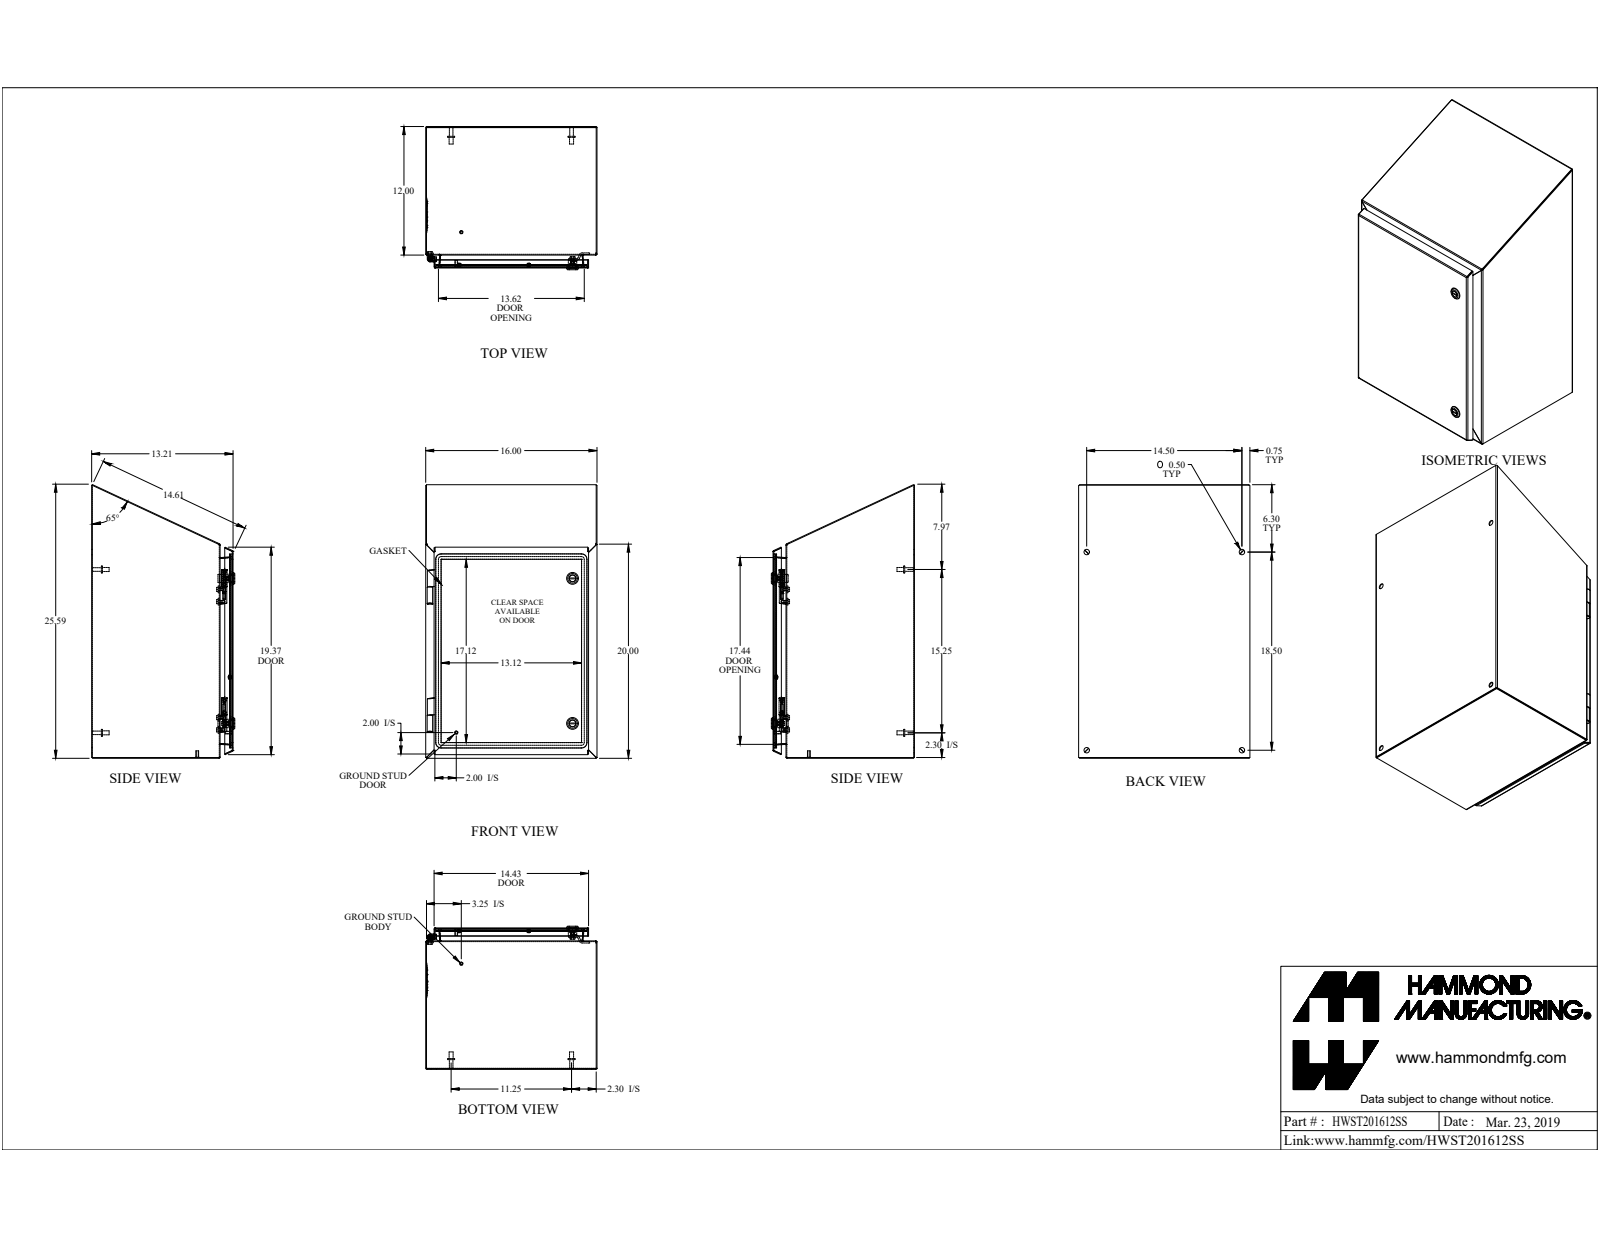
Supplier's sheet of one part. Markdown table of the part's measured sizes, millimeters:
| quantity | value |
| --- | --- |
| part name | HWST201612S16 |
| STEP written by | SolidWorks 2019 (AUTOMOTIVE_DESIGN) |
| units | millimeters |
| bodies | 44 solids, 1121 faces (677 planar, 286 cylindrical, 158 other) |
| overall size | 648.8 × 406.4 × 339.6 |
| volume | 2 401 000 mm³ |
| surface area | 2 563 000 mm² |
| round holes (diameter × count) | 6.1 × 8, 12.7 × 6, 4.9 × 4, 4.9 × 4, 7 × 4, 3.3 × 2, 5 × 2, 9.8 × 2, 16 × 2, 19.5 × 2, 6.1 × 1, 88.9 × 1 |
| round bosses / shafts (diameter × count) | 5.7 × 8, 15.9 × 6, 16.5 × 4, 9.5 × 4, 8.4 × 4, 6.4 × 4, 6 × 3, 27.9 × 2 |
| partial cylindrical surfaces (radius × count) | 6.4 × 24, 0.9 × 18, 2.7 × 18, 1 × 16, 0.3 × 12, 3.2 × 12, 0.8 × 6, 3.4 × 6 |
| main face-to-face distances | 1.8, 404.6, 331.9, 333.7, 402.7, 1.8, 406.4, 333.7, 335.5, 303 |
| hole center spacings | 29, 304.1, 275.2, 304.3, 333.1, 339.4, 368.3, 387.7 |
